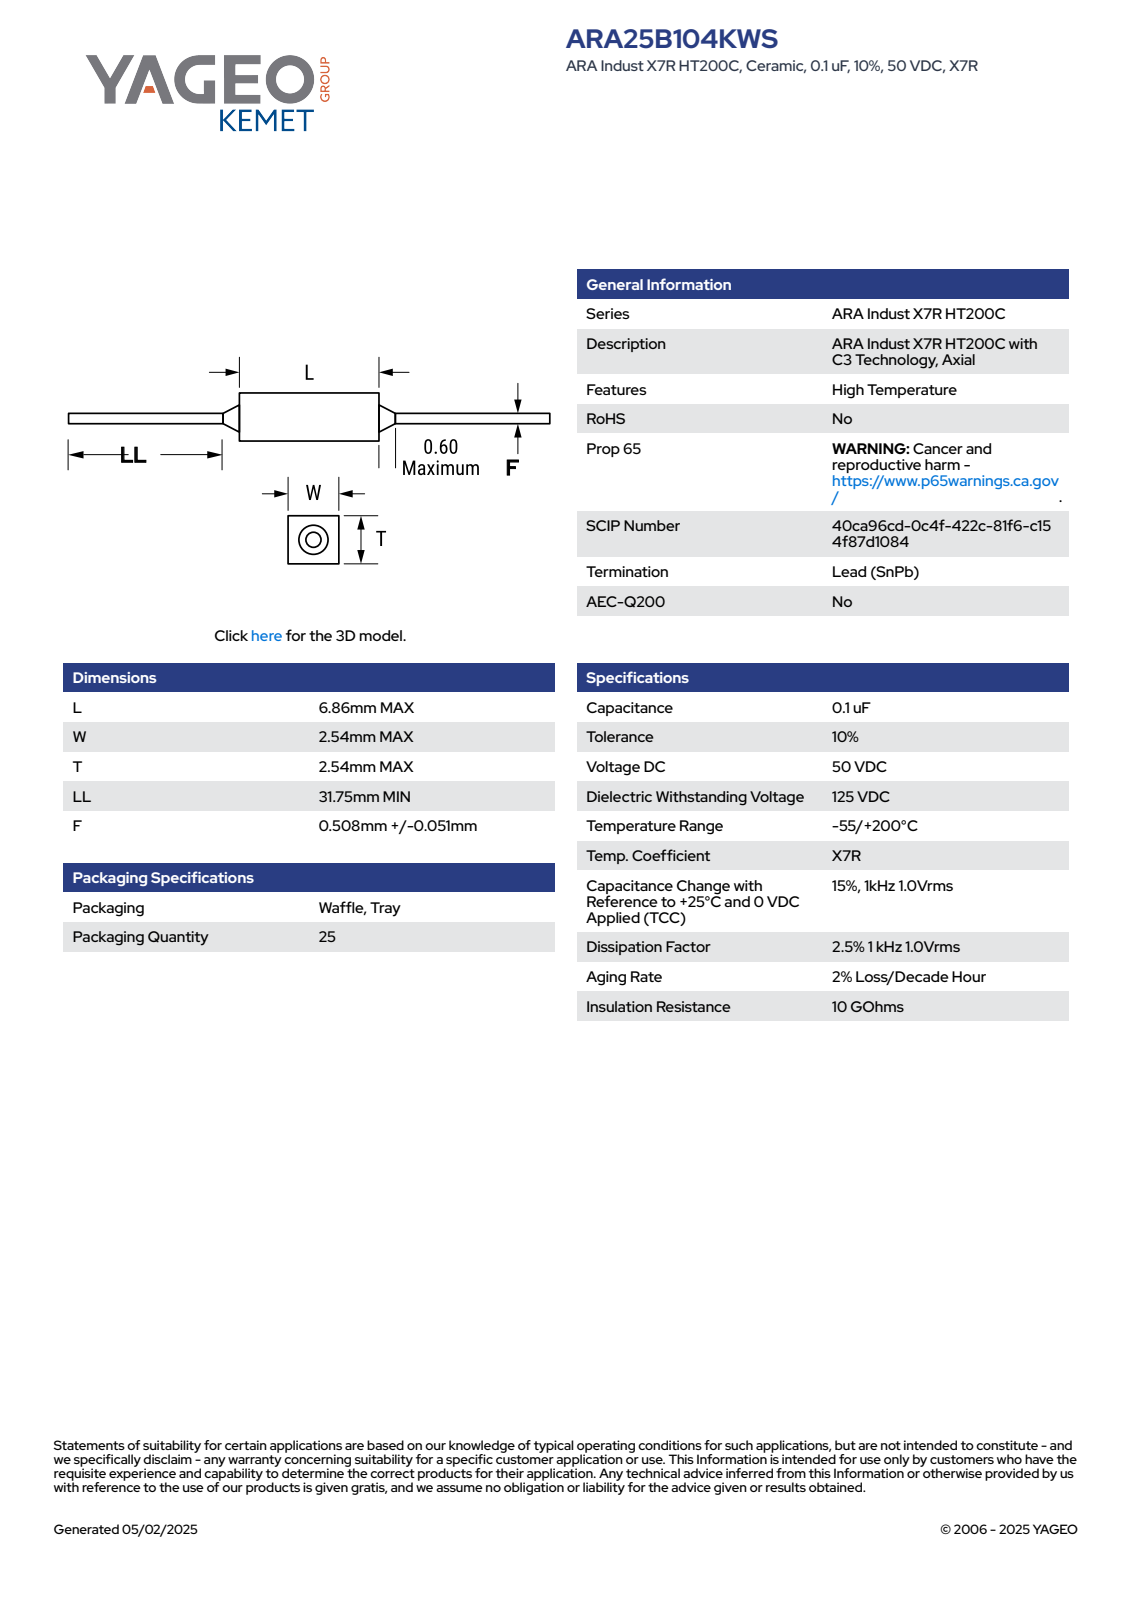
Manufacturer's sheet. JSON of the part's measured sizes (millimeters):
{"part_name": "CCR_C3_25_L6.86T2.54LL3.175F0.559W2.54", "step_written_by": "SolidWorks 2021 (AUTOMOTIVE_DESIGN)", "units": "millimeters", "bodies": {"solids": 4, "faces": 73, "planar": 65, "cylindrical": 4, "other": 4}, "overall_size": [13.68, 2.54, 2.54], "volume_mm3": 46, "surface_area_mm2": 101, "round_bosses_or_shafts": [[0.56, 1]], "face_to_face_distances": [2.54, 6.86, 3.41, 10.27, 13.68, 1.77, 0.77, 0.7, 1.07, 1.84]}
